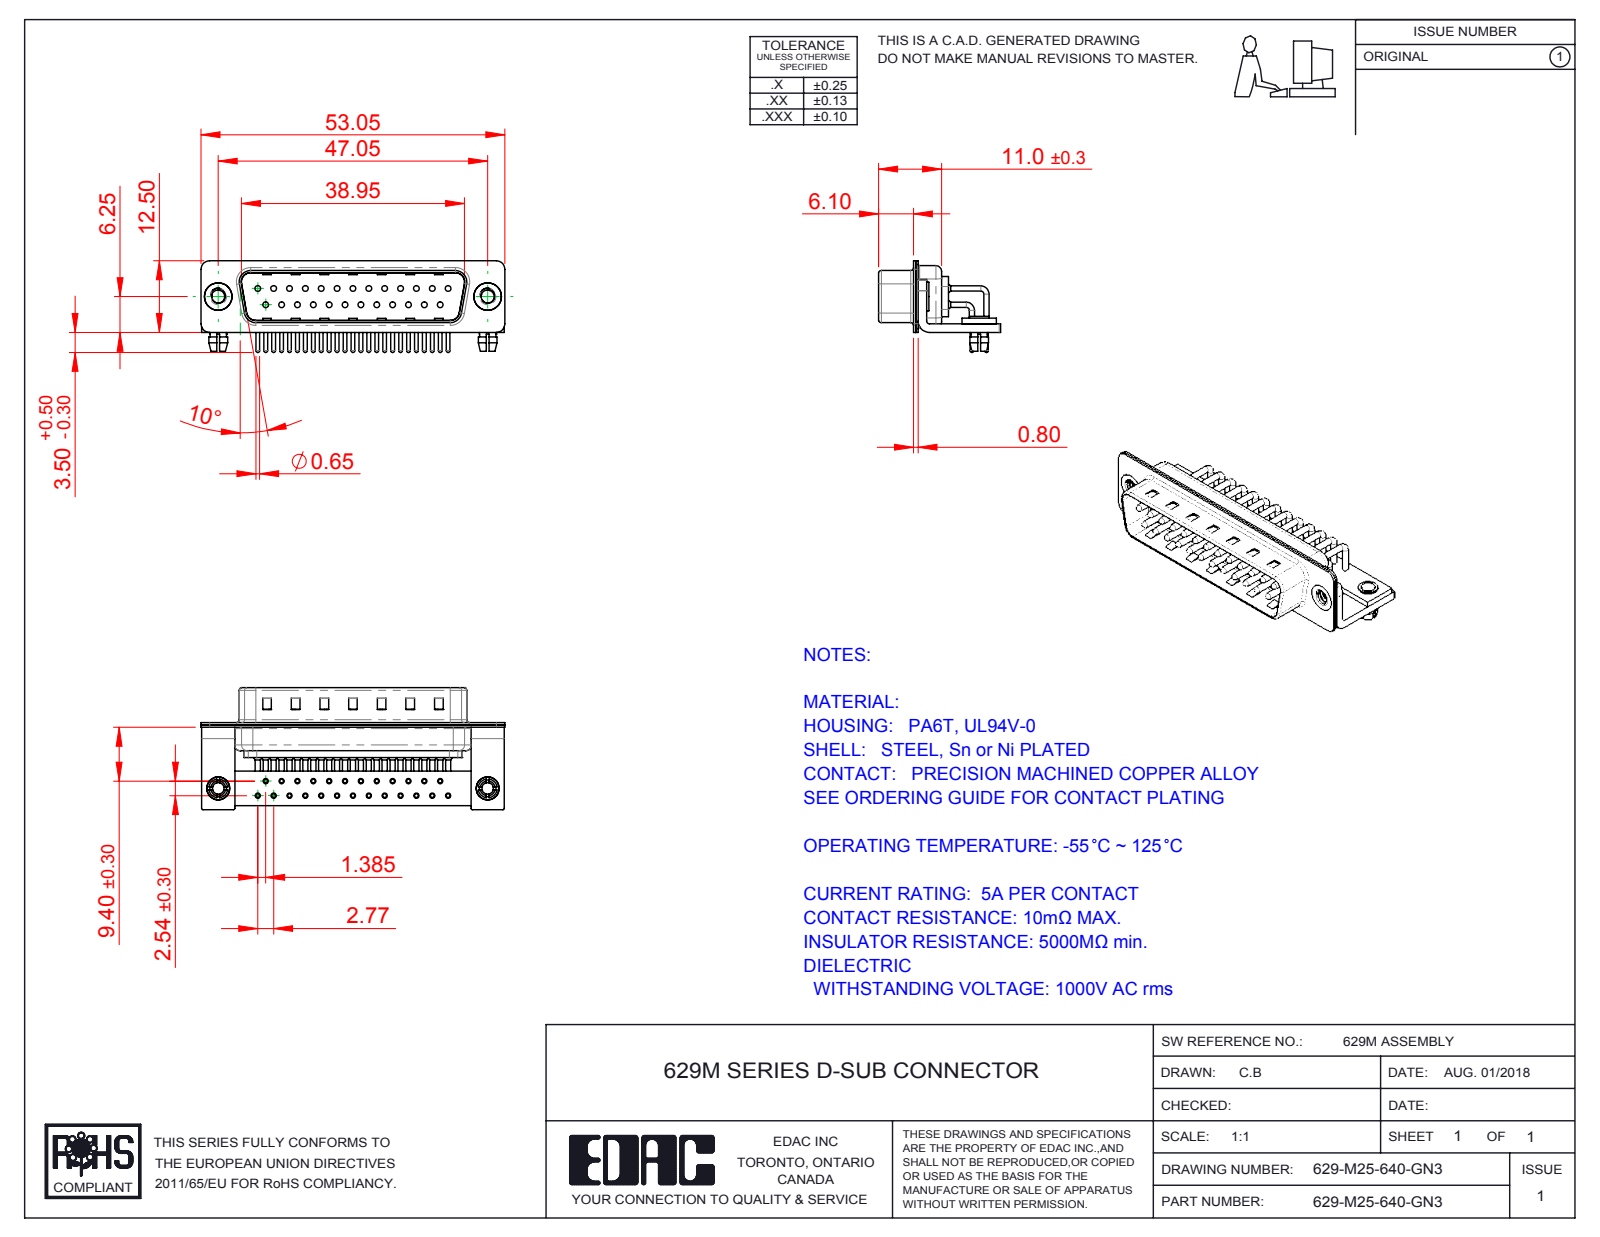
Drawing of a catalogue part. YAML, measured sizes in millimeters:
part_name: "629M Stabilizer Bracket; 629-M25-640-GN3; 629M Contact Row 2; 629M Contact Row 1 (+6 more)"
step_written_by: "SolidWorks 2016 (CONFIG_CONTROL_DESIGN)"
units: millimeters
bodies: {solids: 35, faces: 3318, planar: 1845, cylindrical: 1141, other: 332}
overall_size: [53.05, 21.3, 16]
volume: 3509
surface_area: 9368
round_holes:
  - {diameter: 2, count: 27}
  - {diameter: 0.9, count: 25}
  - {diameter: 1, count: 25}
  - {diameter: 1.7, count: 25}
  - {diameter: 2.26, count: 2}
  - {diameter: 2.5, count: 2}
  - {diameter: 3.2, count: 2}
  - {diameter: 4, count: 2}
  - {diameter: 4.8, count: 2}
round_bosses_or_shafts:
  - {diameter: 1.5, count: 25}
  - {diameter: 0.9, count: 25}
  - {diameter: 0.65, count: 25}
  - {diameter: 5, count: 2}
  - {diameter: 4.9, count: 2}
  - {diameter: 4, count: 2}
  - {diameter: 3.4, count: 2}
  - {diameter: 3.3, count: 2}
partial_cylinders:
  - {radius: 1.01, count: 25}
  - {radius: 0.25, count: 16}
  - {radius: 1.5, count: 16}
  - {radius: 2, count: 13}
  - {radius: 0.5, count: 9}
  - {radius: 1.6, count: 8}
  - {radius: 0.6, count: 4}
  - {radius: 0.65, count: 4}
face_to_face_distances: [0.4, 0.85, 1.25, 1.5, 0.8, 9.55, 10.4, 1, 1.9, 8.3]
hole_center_spacings: [2.77, 5.54, 8.31, 11.08, 13.85, 3.16, 4.87, 16.62]
